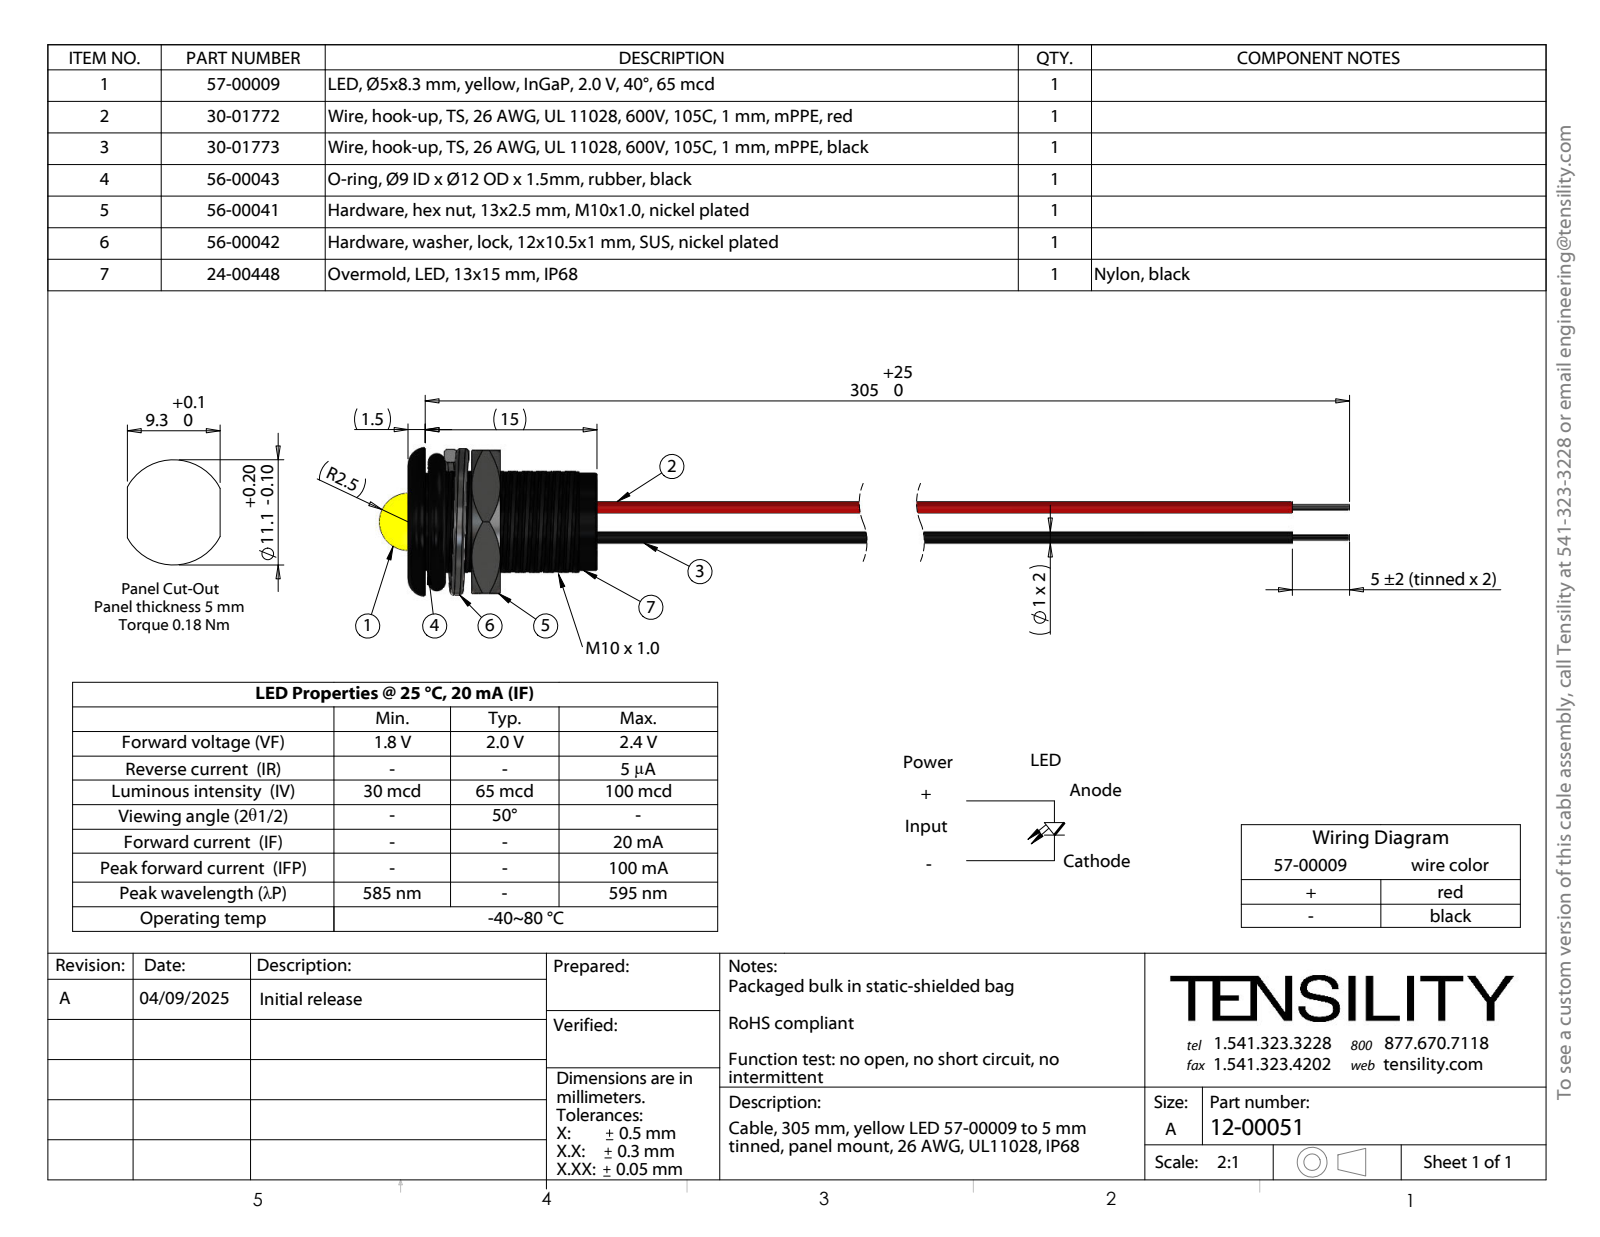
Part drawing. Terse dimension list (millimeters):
name: 12-00051; 24-00448; 30-01772_stripped and tinned; 56-00042_Split washer (+4 more)
written by: SolidWorks 2021 (CONFIG_CONTROL_DESIGN)
unit: mm
bodies: 57 solids, 514 faces (185 planar, 246 cylindrical, 83 other)
size: 173.99 × 14.43 × 12.99
volume: 1 769 mm³; area: 6 568 mm²
holes: 2× ⌀1
bosses: 2× ⌀1, 2× ⌀0.83, 1× ⌀8.5, 1× ⌀5
rounds: 1× R4.33, 1× R5
face distances: 1.5, 16.5, 15, 12.5, 8.06, 6.56, 8.44, 5.56, 4.06, 2.5
hole spacings: 0.36, 0.38, 0.33, 2.43, 2.35, 2.48, 2.52, 2.56
